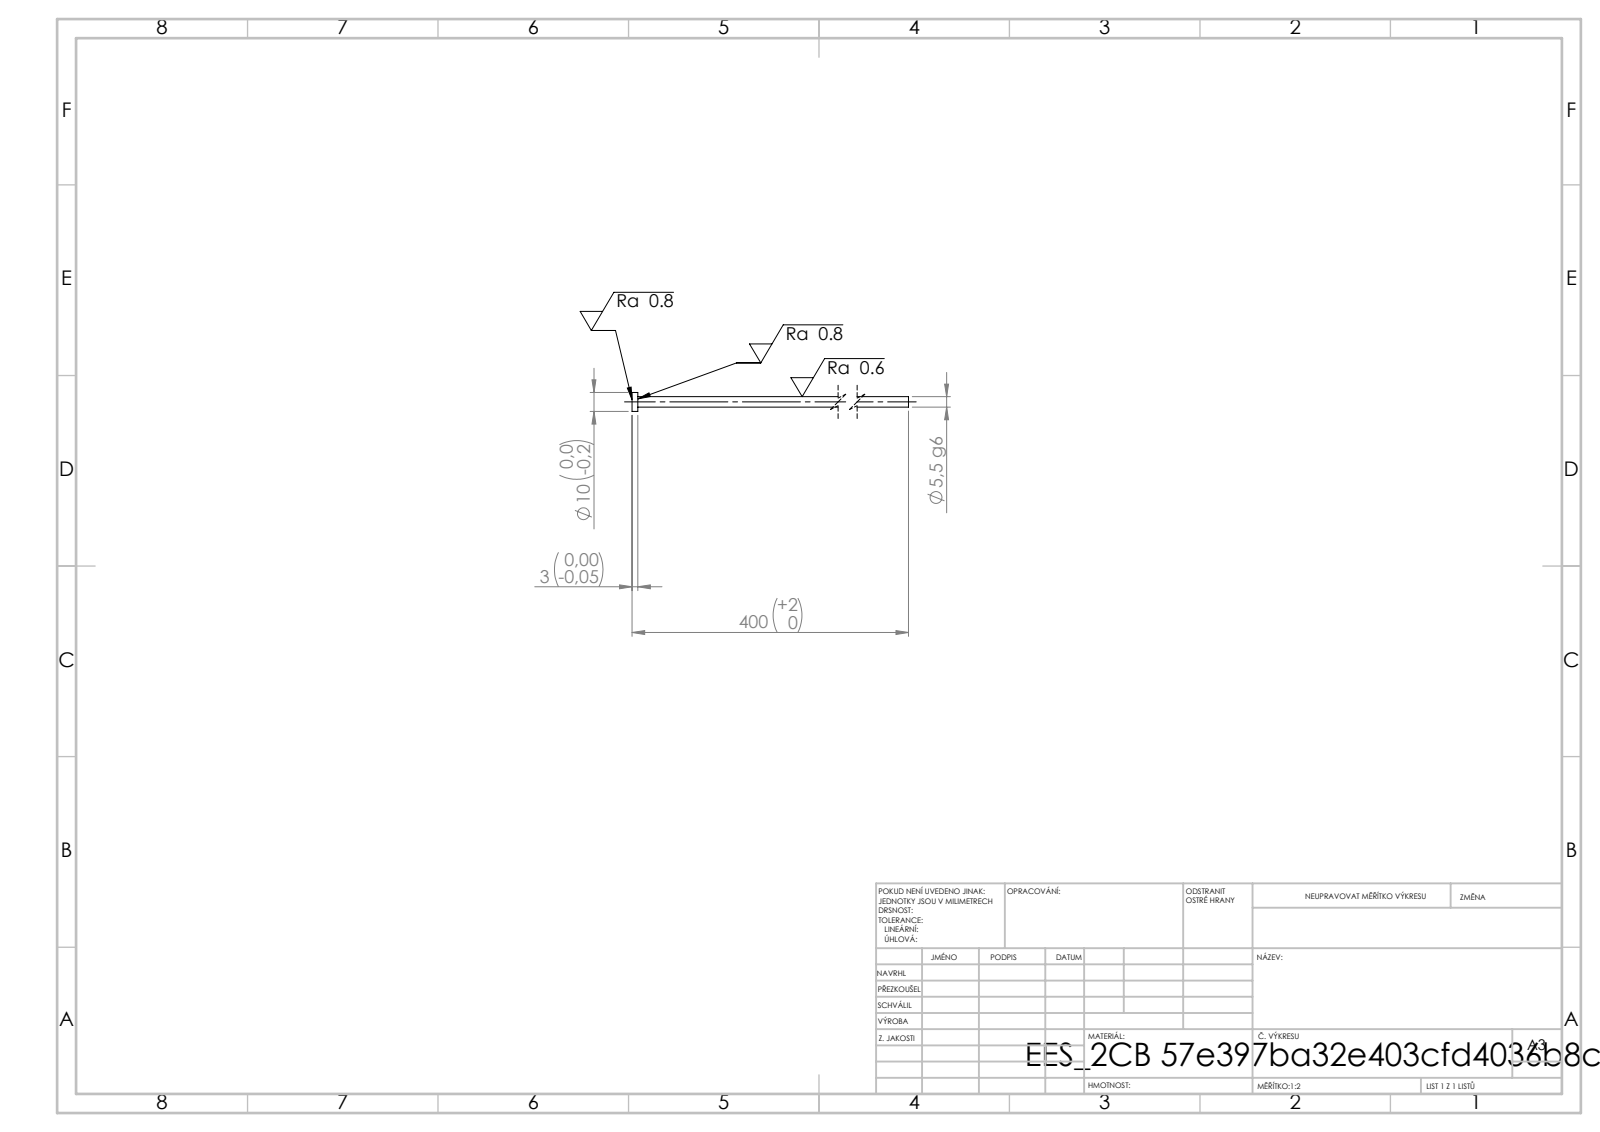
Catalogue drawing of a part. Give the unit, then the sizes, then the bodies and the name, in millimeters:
Units: millimetres
Overall size (bounding box): 400 × 10 × 10
Round bosses / shafts (diameter × count): ⌀10 ×1, ⌀5.5 ×1
Main face-to-face distances: 3, 400, 397
Volume: 9 668 mm³ · Surface area: 7 111 mm²
Bodies: 1 solid, 7 faces (3 planar, 4 cylindrical, 0 other)
STEP written by: SolidWorks 2019 (CONFIG_CONTROL_DESIGN)
